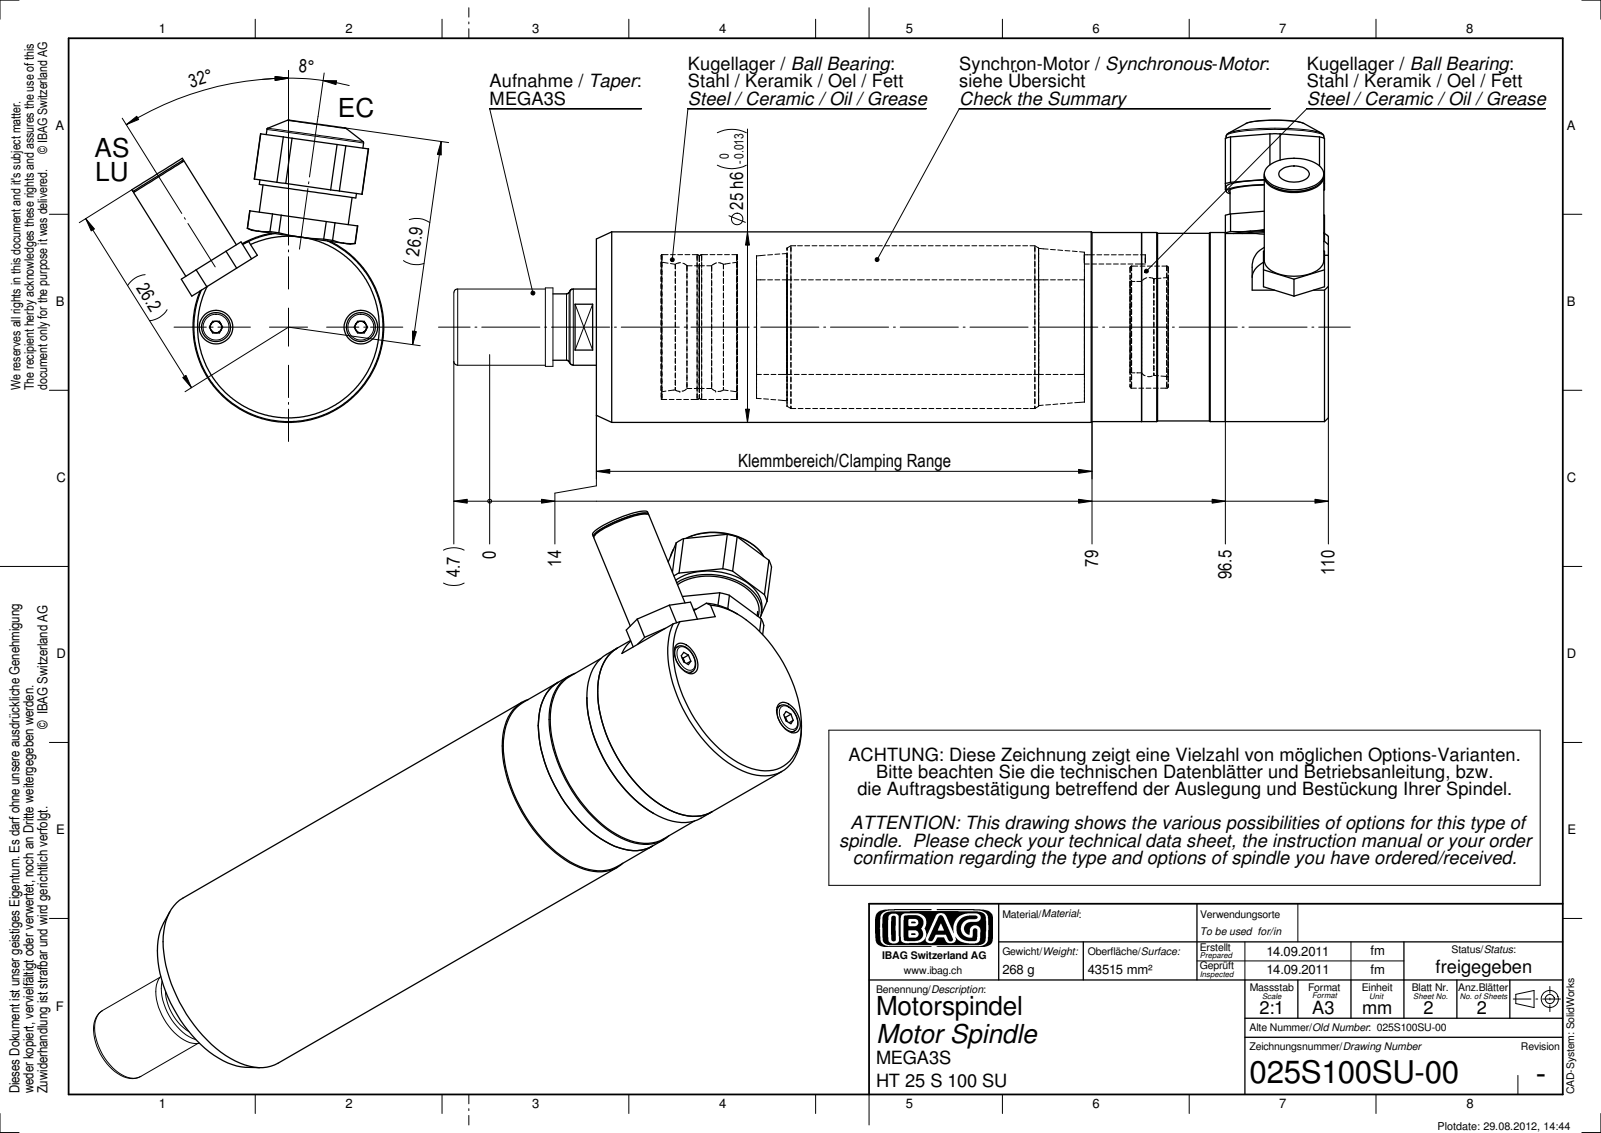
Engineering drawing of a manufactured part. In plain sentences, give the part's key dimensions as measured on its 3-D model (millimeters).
The part is named "025S100SU-00". Its 3-D file was written by "SolidWorks 2010 (CONFIG_CONTROL_DESIGN)". It is 0 solids with 194 faces: 77 planar, 68 cylindrical and 49 other. Overall it measures 114.7 by 39.65 by 33.04 millimeters. Round holes: 2 of diameter 4, 2 of diameter 4.4, 1 of diameter 3, 1 of diameter 3.3, 1 of diameter 6.2, 1 of diameter 10.6. Round bosses or shafts: 2 of diameter 3.8, 1 of diameter 25, 1 of diameter 24.8, 1 of diameter 24.6, 1 of diameter 22.6, 1 of diameter 12.8, 1 of diameter 11.79, 1 of diameter 10.3. Partial cylindrical surfaces (rounded edges, fillets, slot ends): 2 of radius 7.15, 1 of radius 5.5. The main face-to-face distances are 96, 1.8, 94.2, 71.5, 69.7, 24.5, 13, 11, 82.5, 80.7. The hole center spacings are 9.5, 19.
